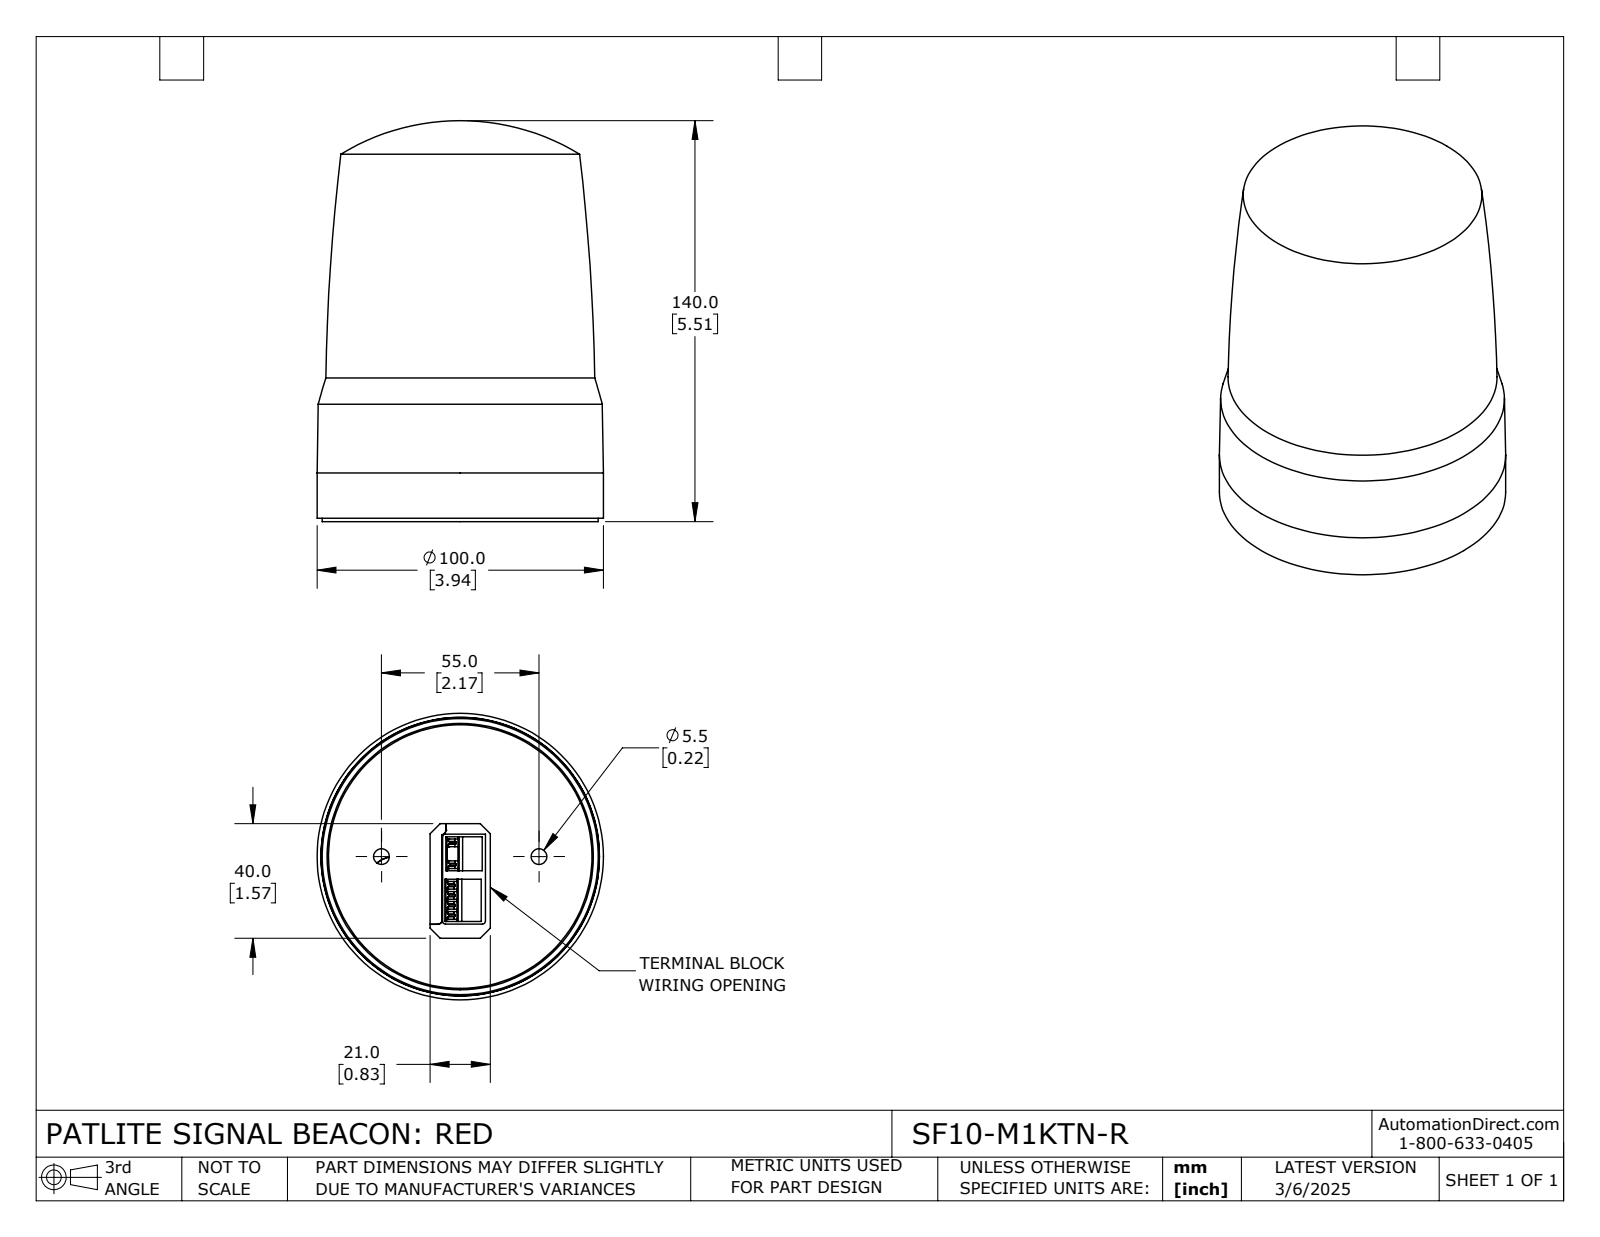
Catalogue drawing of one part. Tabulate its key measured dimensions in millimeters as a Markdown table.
| quantity | value |
| --- | --- |
| part name | SF10-M1KTN-R |
| STEP written by | SolidWorks 2024 (CONFIG_CONTROL_DESIGN) |
| units | millimeters |
| bodies | 2 solids, 268 faces (183 planar, 29 cylindrical, 56 other) |
| overall size | 140 × 100 × 100 |
| volume | 857 676 mm³ |
| surface area | 76 986 mm² |
| round holes (diameter × count) | 5.5 × 2, 13 × 2, 93 × 1, 95.6 × 1 |
| round bosses / shafts (diameter × count) | 100 × 1, 96.4 × 1, 94.5 × 1, 93.2 × 1, 92 × 1 |
| partial cylindrical surfaces (radius × count) | 0.3 × 2, 44.32 × 1, 44.75 × 1 |
| main face-to-face distances | 6.3, 14.7, 8.4, 1.5, 6.9, 13.2, 12.6, 3.15, 4.4, 7 |
| hole center spacings | 27.5, 55 |
